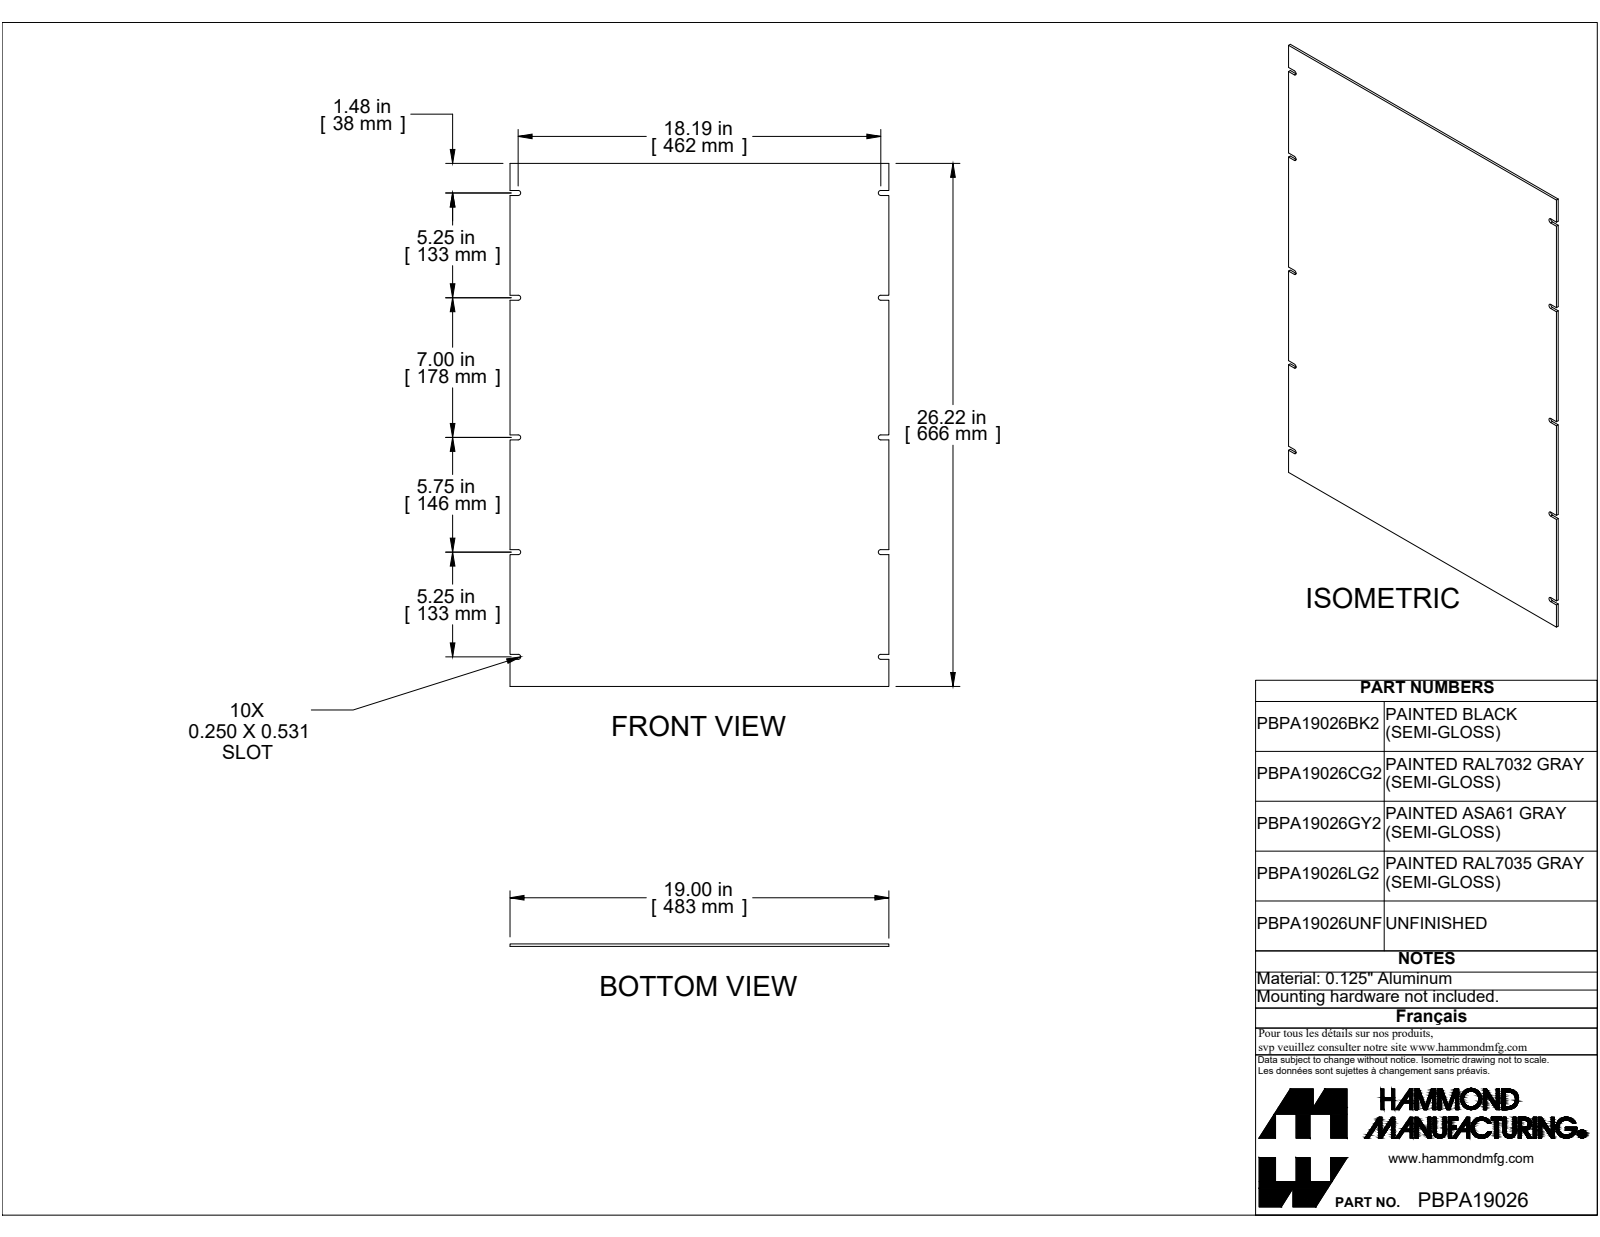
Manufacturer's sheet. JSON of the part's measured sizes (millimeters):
{"part_name": "PBPA19026GY2", "step_written_by": "SolidWorks 2019 (CONFIG_CONTROL_DESIGN)", "units": "millimeters", "bodies": {"solids": 1, "faces": 46, "planar": 36, "cylindrical": 10, "other": 0}, "overall_size": [665.9, 482.6, 3.2], "volume_mm3": 1018000, "surface_area_mm2": 649000, "partial_cylinders_radius": [[3.2, 10]], "face_to_face_distances": [3.2, 482.6, 665.9, 6.4, 133.4, 457.2, 139.7, 34.5, 40.9, 167.9]}
